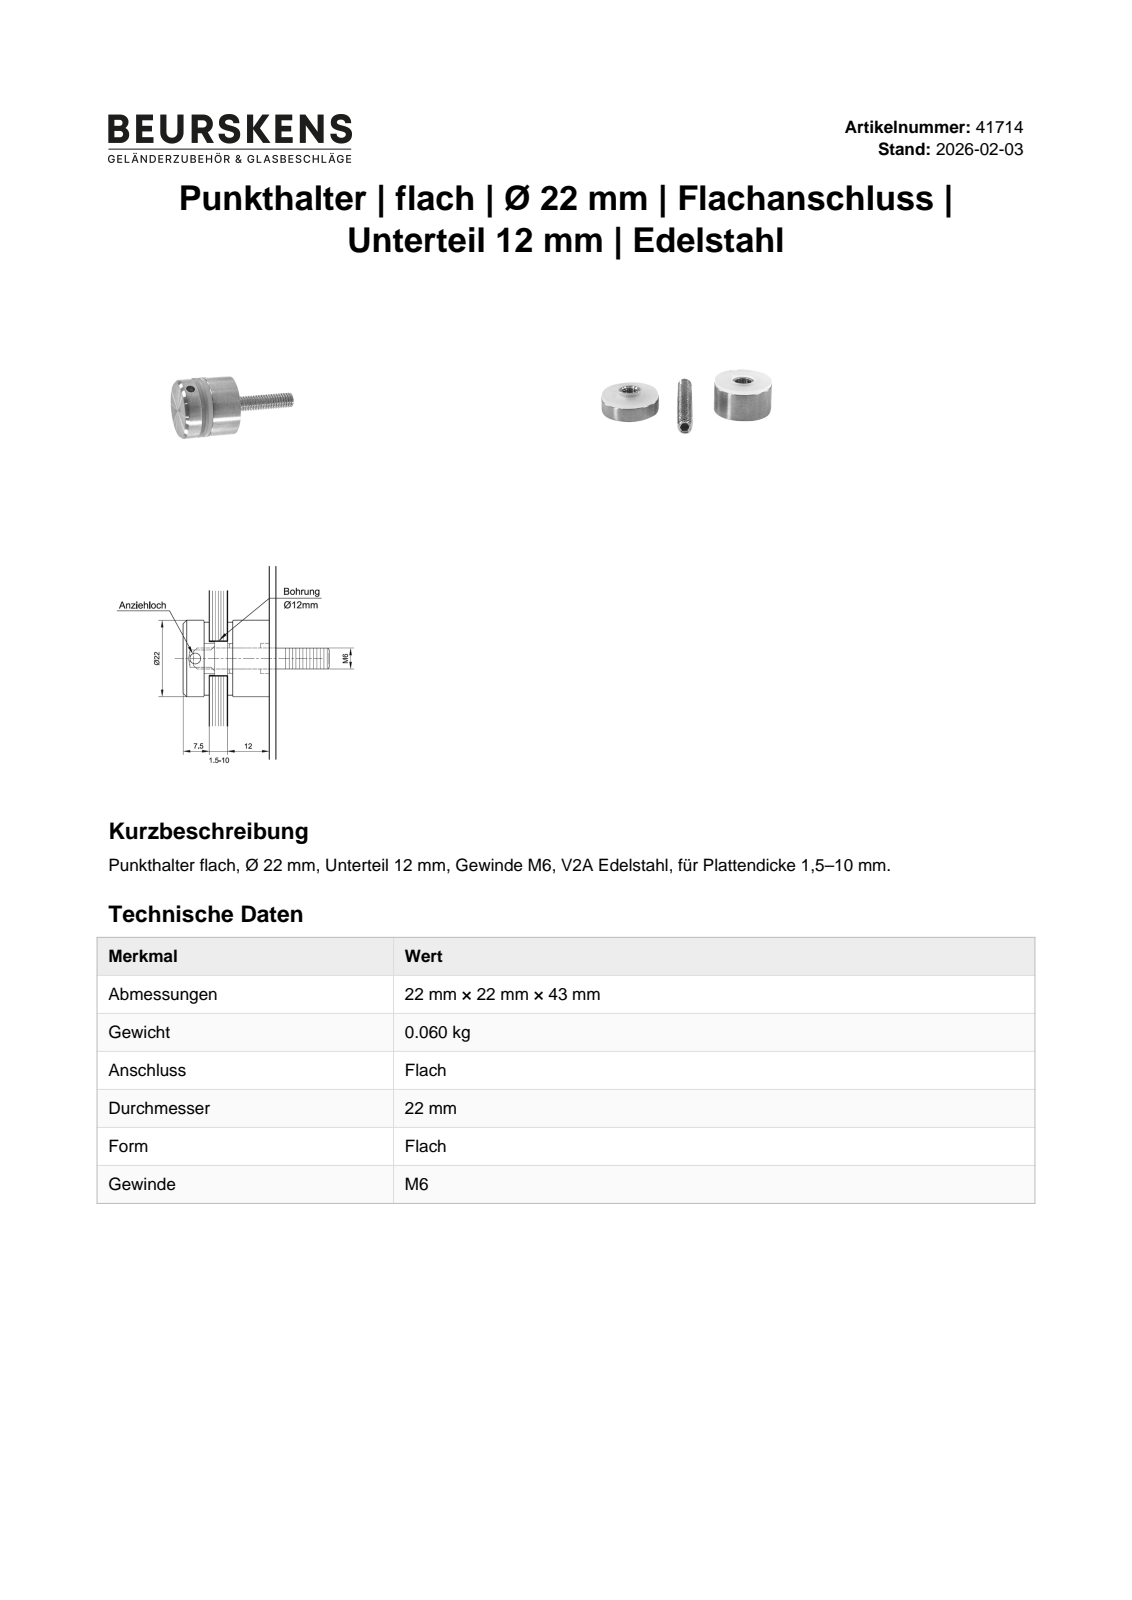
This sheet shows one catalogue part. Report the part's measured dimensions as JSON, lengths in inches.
{"part_name": "41714; 40923; 40913; Gewindestift M6x40mm (+2 more)", "step_written_by": "Autodesk Inventor 2023 (AUTOMOTIVE_DESIGN)", "units": "inches", "bodies": {"solids": 5, "faces": 41, "planar": 23, "cylindrical": 14, "other": 4}, "overall_size": [1.673, 0.866, 0.866], "volume_in3": 0.476, "surface_area_in2": 8.421, "round_holes": [[0.118, 1], [0.236, 1], [0.24, 1], [0.335, 1], [0.413, 1]], "round_bosses_or_shafts": [[0.866, 1], [0.827, 1], [0.374, 1]], "face_to_face_distances": [0.059, 0.413, 0.177, 0.118, 0.354, 0.236, 0.295, 0.827, 0.591, 0.472]}
